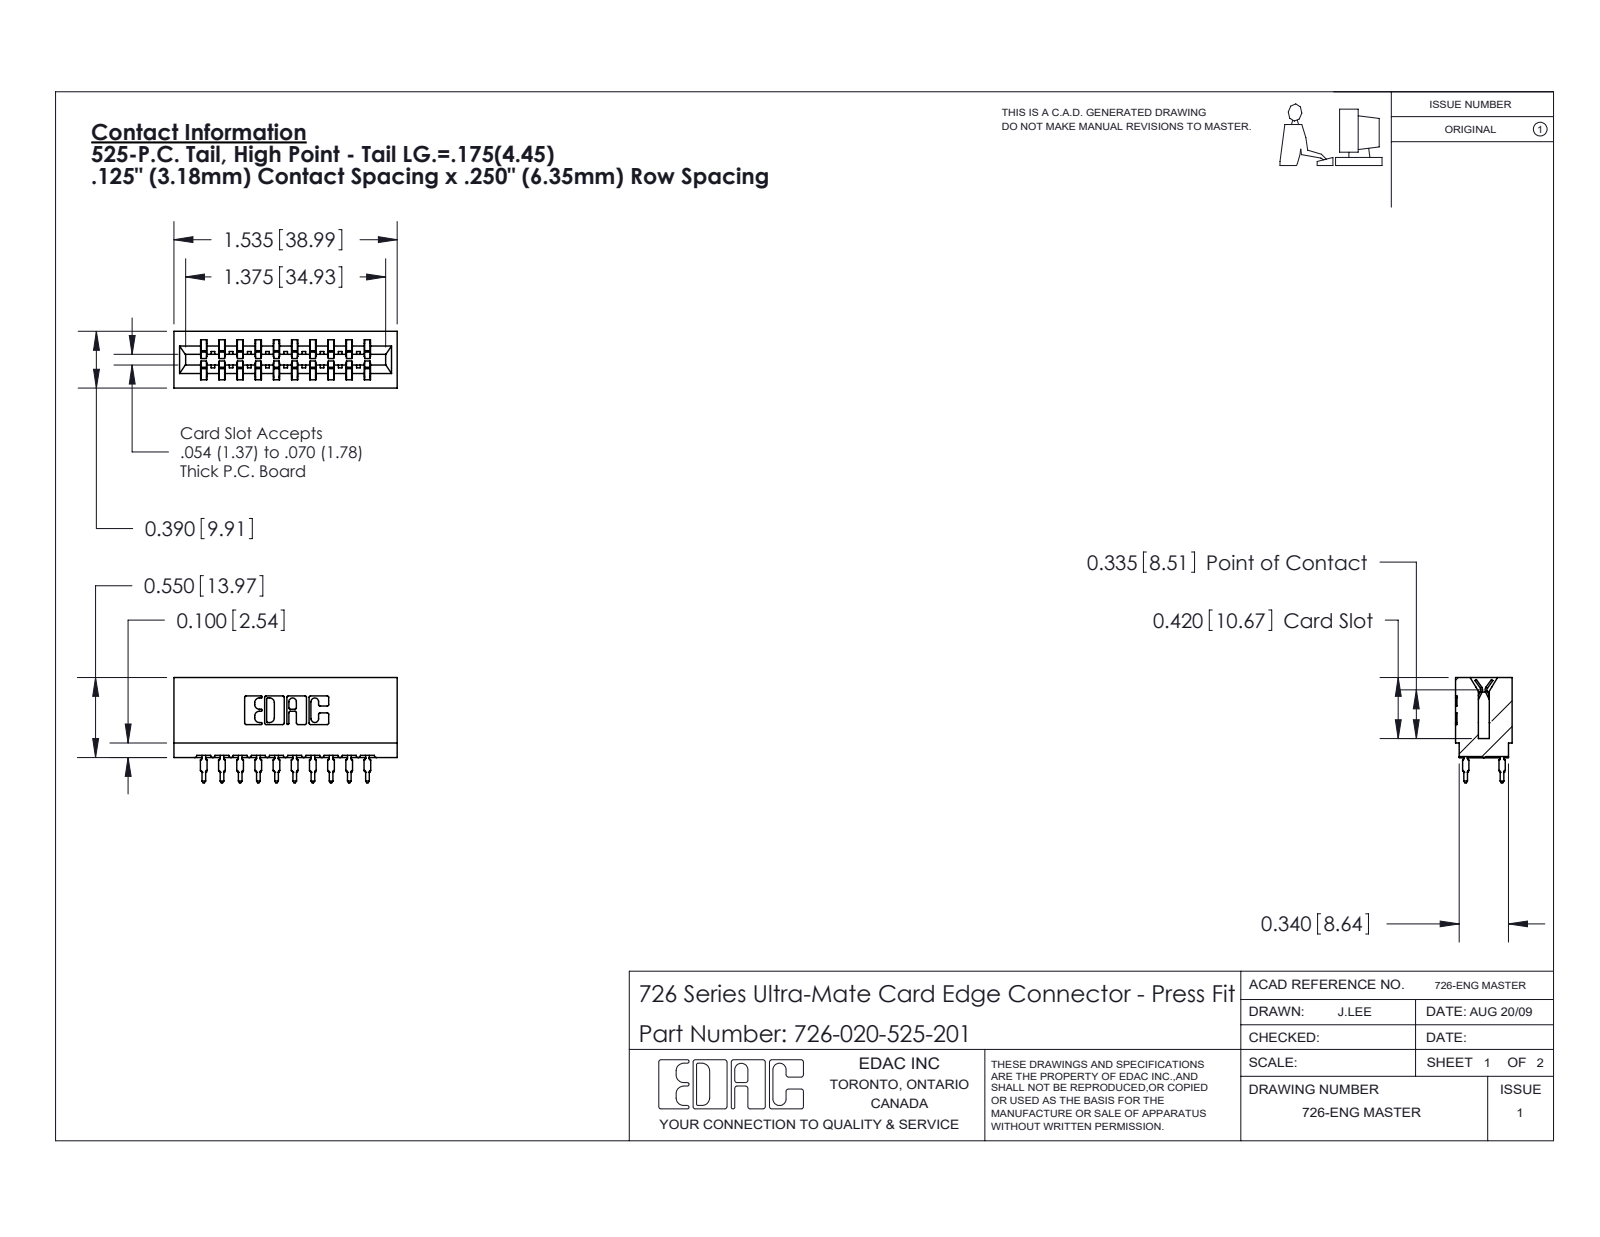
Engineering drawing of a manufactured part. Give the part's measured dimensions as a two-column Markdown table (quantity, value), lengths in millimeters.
| quantity | value |
| --- | --- |
| part name | 726-020-525-201; 746-292-001_525; 726 Part_.515 Slot Depth - 01 |
| STEP written by | SolidWorks 2020 (CONFIG_CONTROL_DESIGN) |
| units | millimeters |
| bodies | 21 solids, 1887 faces (975 planar, 392 cylindrical, 520 other) |
| overall size | 39 × 18.4 × 9.9 |
| volume | 3 750 mm³ |
| surface area | 5 631 mm² |
| partial cylindrical surfaces (radius × count) | 0.5 × 40, 0.3 × 22, 0.4 × 11, 0.1 × 8, 0.3 × 8, 0.2 × 6, 0.8 × 6, 0.7 × 3 |
| main face-to-face distances | 6.4, 1.4, 8.5, 3.2, 1.1, 19.1, 12.7, 9.9, 7.4, 9.5 |
